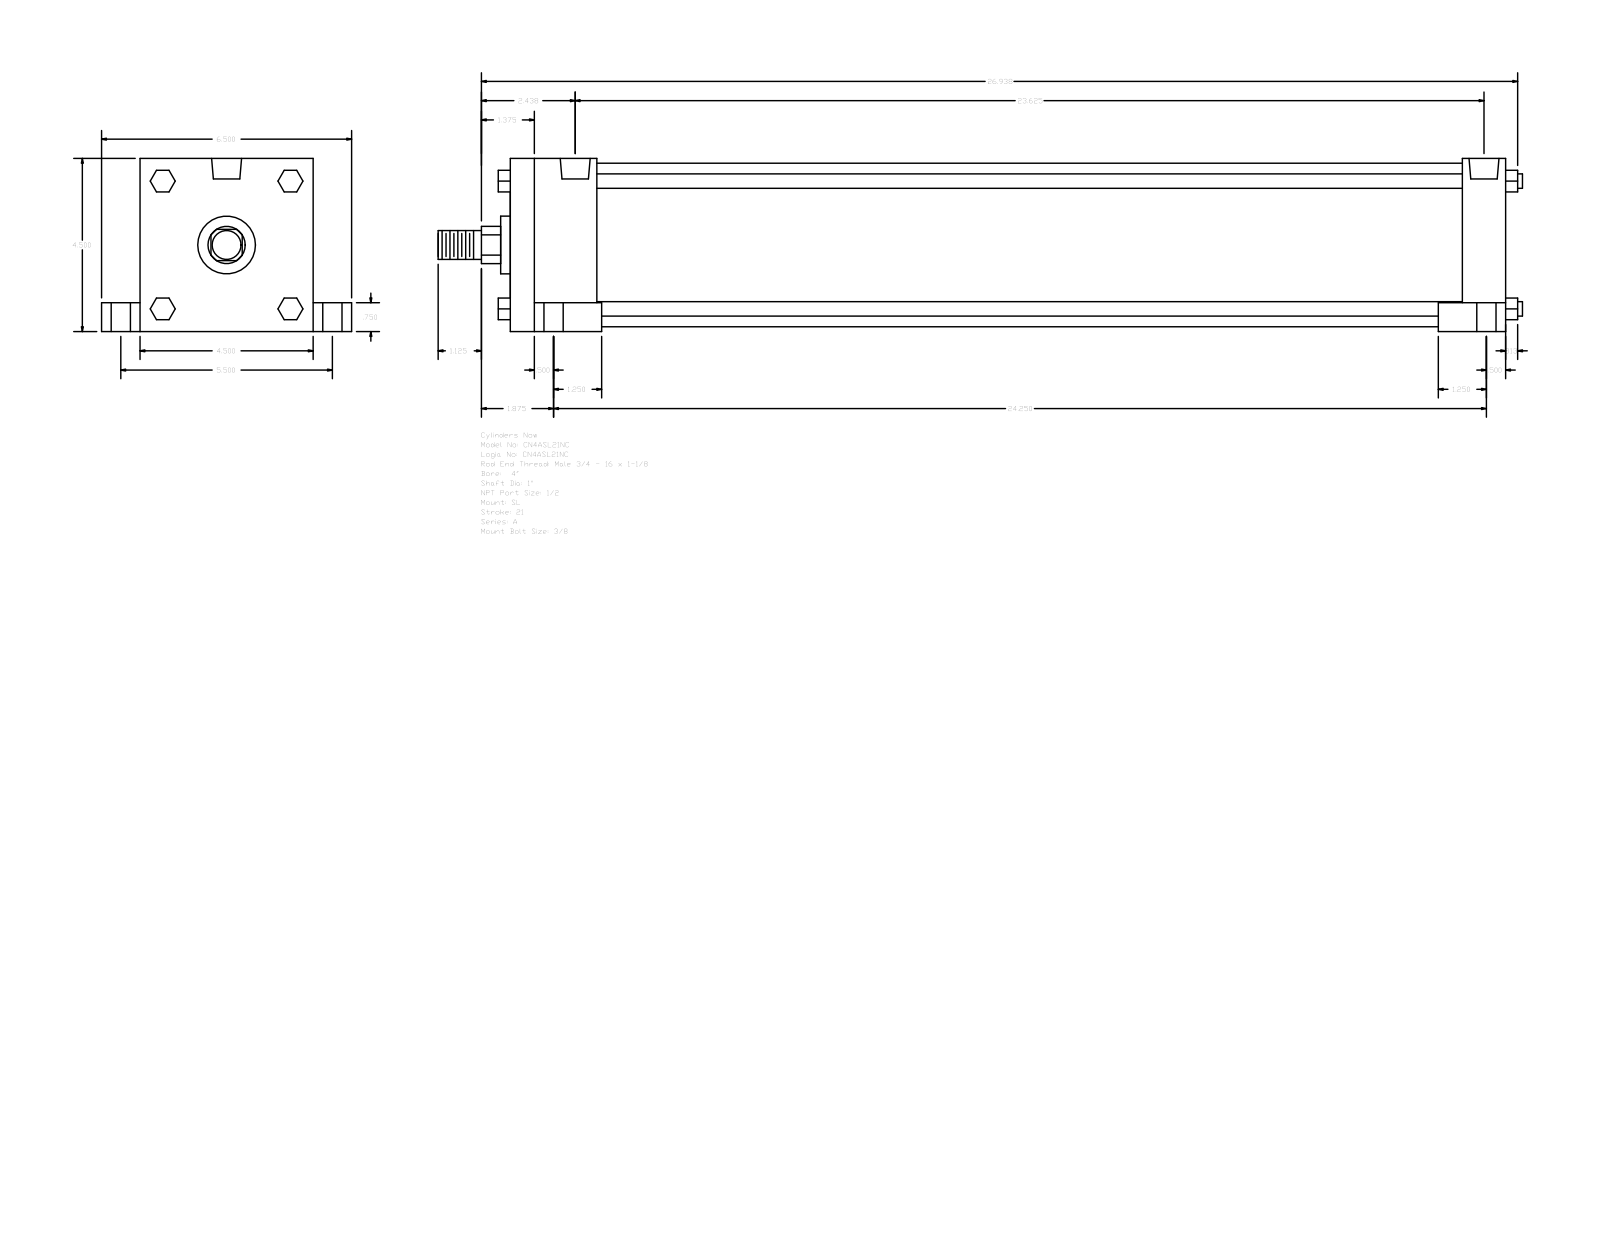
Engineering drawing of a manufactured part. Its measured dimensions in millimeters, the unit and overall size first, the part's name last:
Units: millimetres
Overall size (bounding box): 715.96 × 165.1 × 114.3
Round holes (diameter × count): ⌀8.73 ×4, ⌀12.7 ×4, ⌀19.05 ×4, ⌀19.77 ×2
Round bosses / shafts (diameter × count): ⌀9.53 ×4, ⌀107.95 ×1, ⌀38.1 ×1, ⌀25.4 ×1, ⌀19.05 ×1
Partial cylindrical surfaces — rounded edges, fillets, slot ends (radius × count): R12.29 ×1
Main face-to-face distances: 114.3, 657.22, 28.57, 57.15, 600.07, 628.65, 571.5, 19.05, 25.4, 139.7
Hole centre spacings: 3.18, 69.87, 70.01, 71.3, 72, 139.7, 593.72, 596.9
Bodies: 0 solids, 150 faces (114 planar, 36 cylindrical, 0 other)
Part name (STEP PRODUCT): A_SL__0400_1
STEP written by: GSSL Pune (CONFIG_CONTROL_DESIGN)
